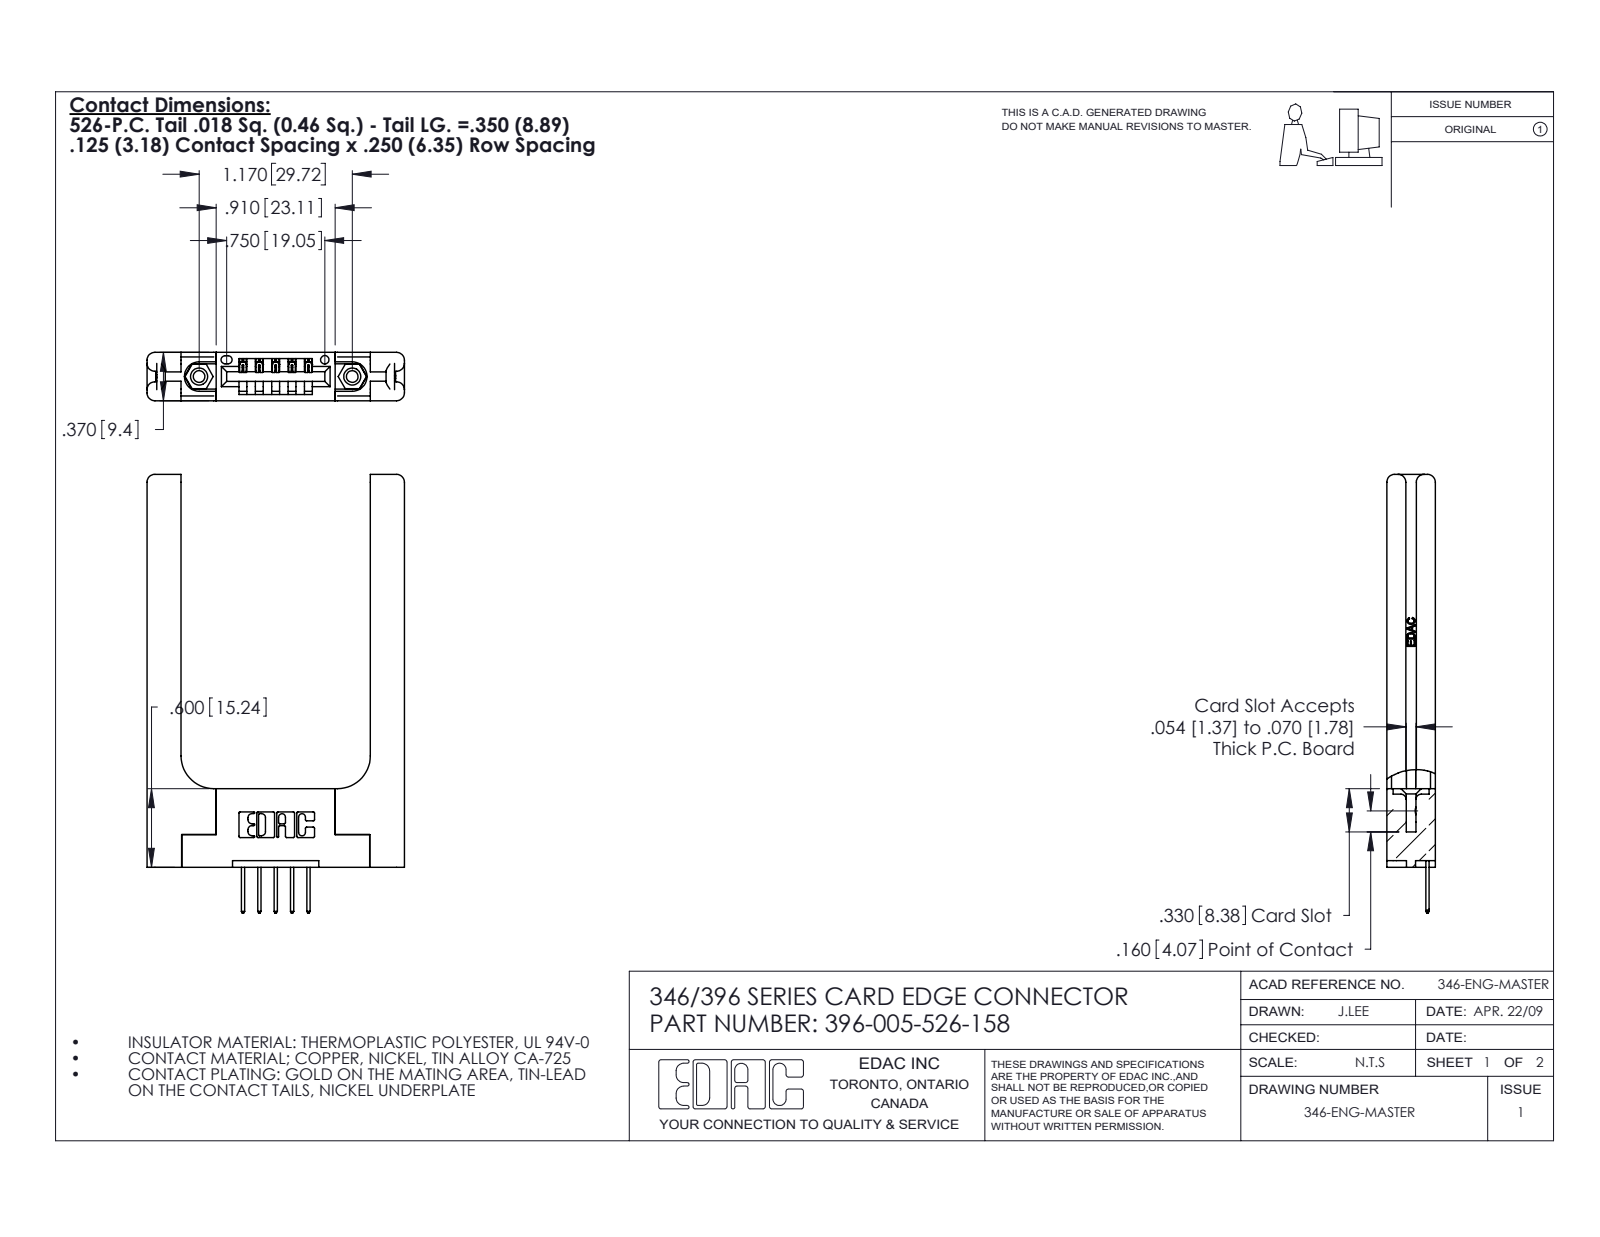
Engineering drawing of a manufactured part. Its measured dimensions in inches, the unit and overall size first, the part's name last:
Units: inches
Overall size (bounding box): 3.35 × 1.966 × 0.37
Round holes (diameter × count): ⌀0.089 ×2, ⌀0.125 ×2, ⌀0.156 ×2, ⌀0.064 ×1
Round bosses / shafts (diameter × count): ⌀0.155 ×2
Partial cylindrical surfaces — rounded edges, fillets, slot ends (radius × count): R0.01 ×22, R0.06 ×16, R0.006 ×10, R0.01 ×10, R0.007 ×6, R0.031 ×6, R0.026 ×3, R0.03 ×2
Main face-to-face distances: 0.37, 0.15, 0.22, 0.072, 0.25, 1.446, 0.148, 0.071, 0.26, 1.706
Hole centre spacings: 0.246, 0.969, 1.17
Volume: 0.734 in³ · Surface area: 16.16 in²
Bodies: 10 solids, 682 faces (438 planar, 184 cylindrical, 60 other)
Part name (STEP PRODUCT): 345-250-001_345-250-001-102; 396-005-526-158; 346-220-058_345-220-058; 345-292-001_345-293-126 (+1 more)
STEP written by: SolidWorks 2020 (CONFIG_CONTROL_DESIGN)
